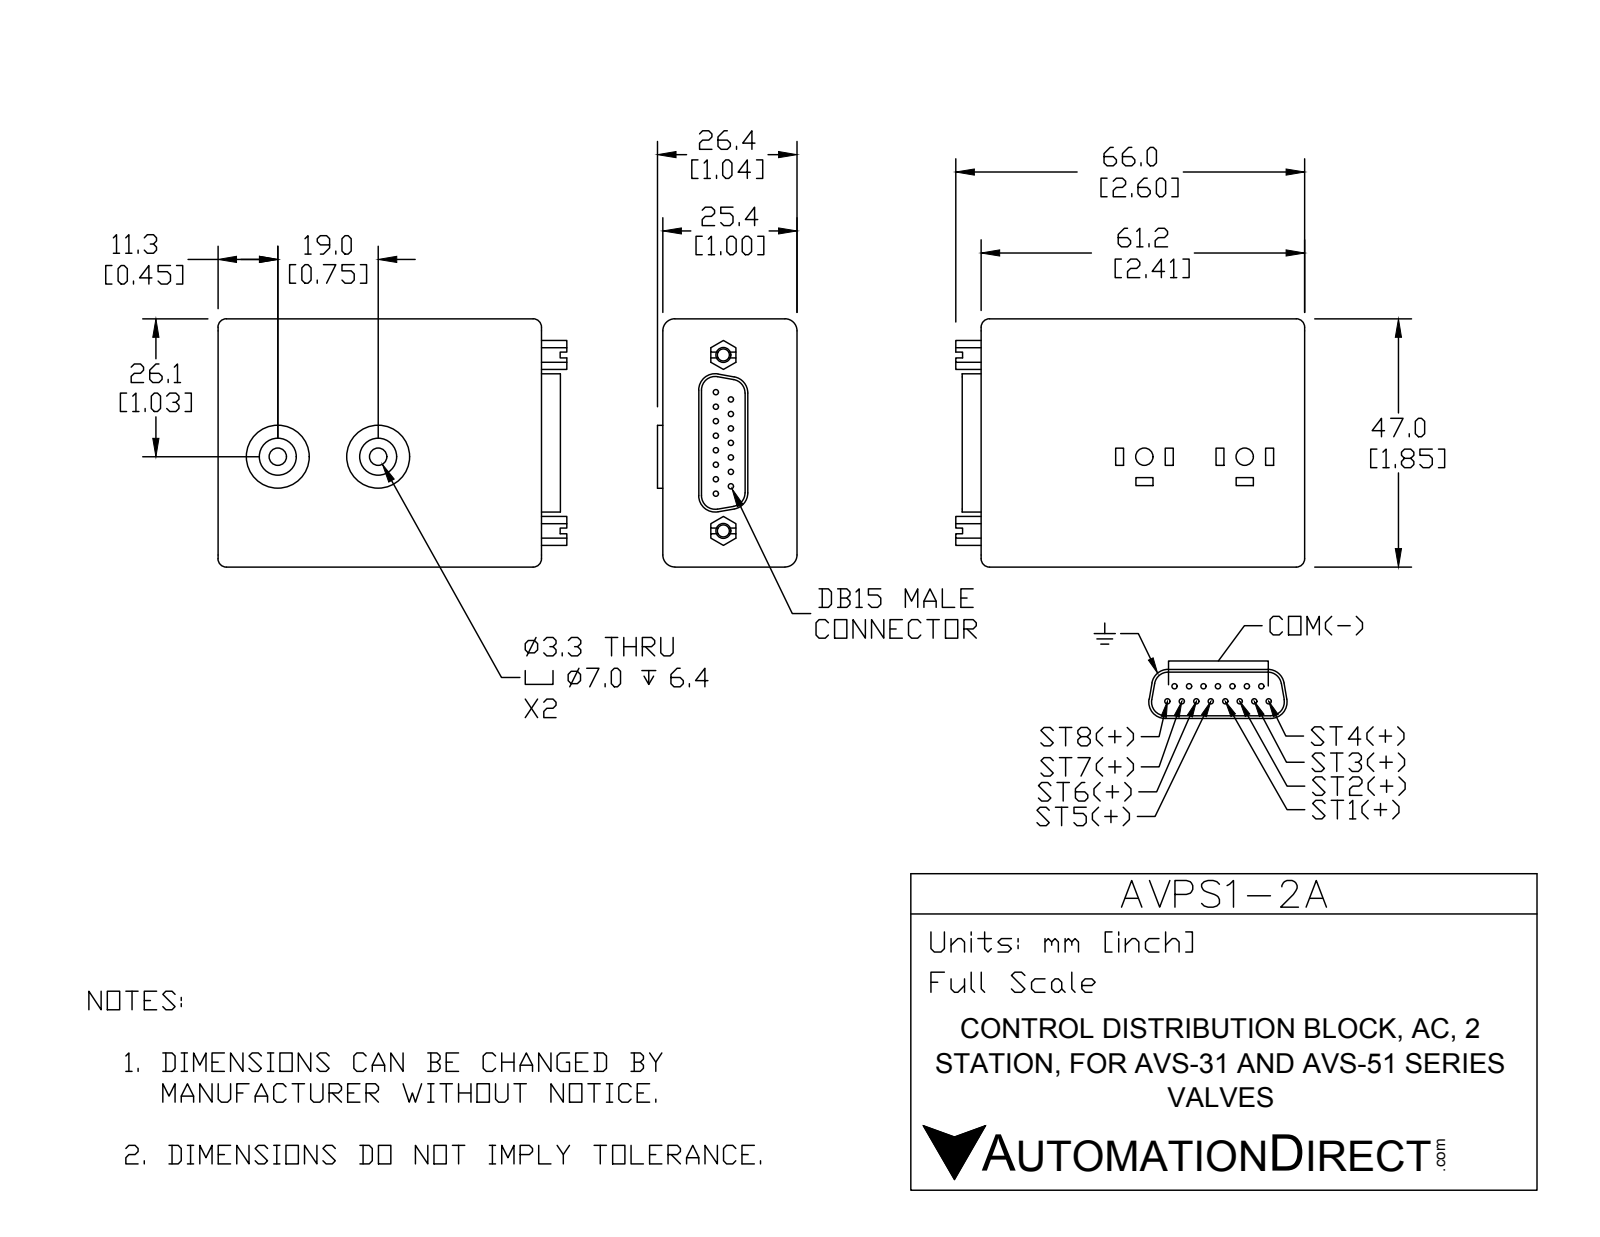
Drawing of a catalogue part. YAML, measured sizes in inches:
part_name: "AVPS1-2A"
step_written_by: "SolidWorks 2016 (AUTOMOTIVE_DESIGN)"
units: inches
bodies: {solids: 1, faces: 173, planar: 93, cylindrical: 68, other: 12}
overall_size: [2.6, 1.85, 1.04]
volume: 4.369
surface_area: 20.21
round_holes:
  - {diameter: 0.089, count: 2}
  - {diameter: 0.13, count: 2}
  - {diameter: 0.275, count: 2}
round_bosses_or_shafts:
  - {diameter: 0.039, count: 15}
  - {diameter: 0.469, count: 2}
partial_cylinders:
  - {radius: 0.062, count: 8}
  - {radius: 0.09, count: 4}
  - {radius: 0.102, count: 4}
  - {radius: 0.122, count: 4}
face_to_face_distances: [1, 1.85, 2.411, 0.123, 2.288, 0.02, 0.04, 1.04, 0.345, 0.328]
hole_center_spacings: [0.748, 1.311]
